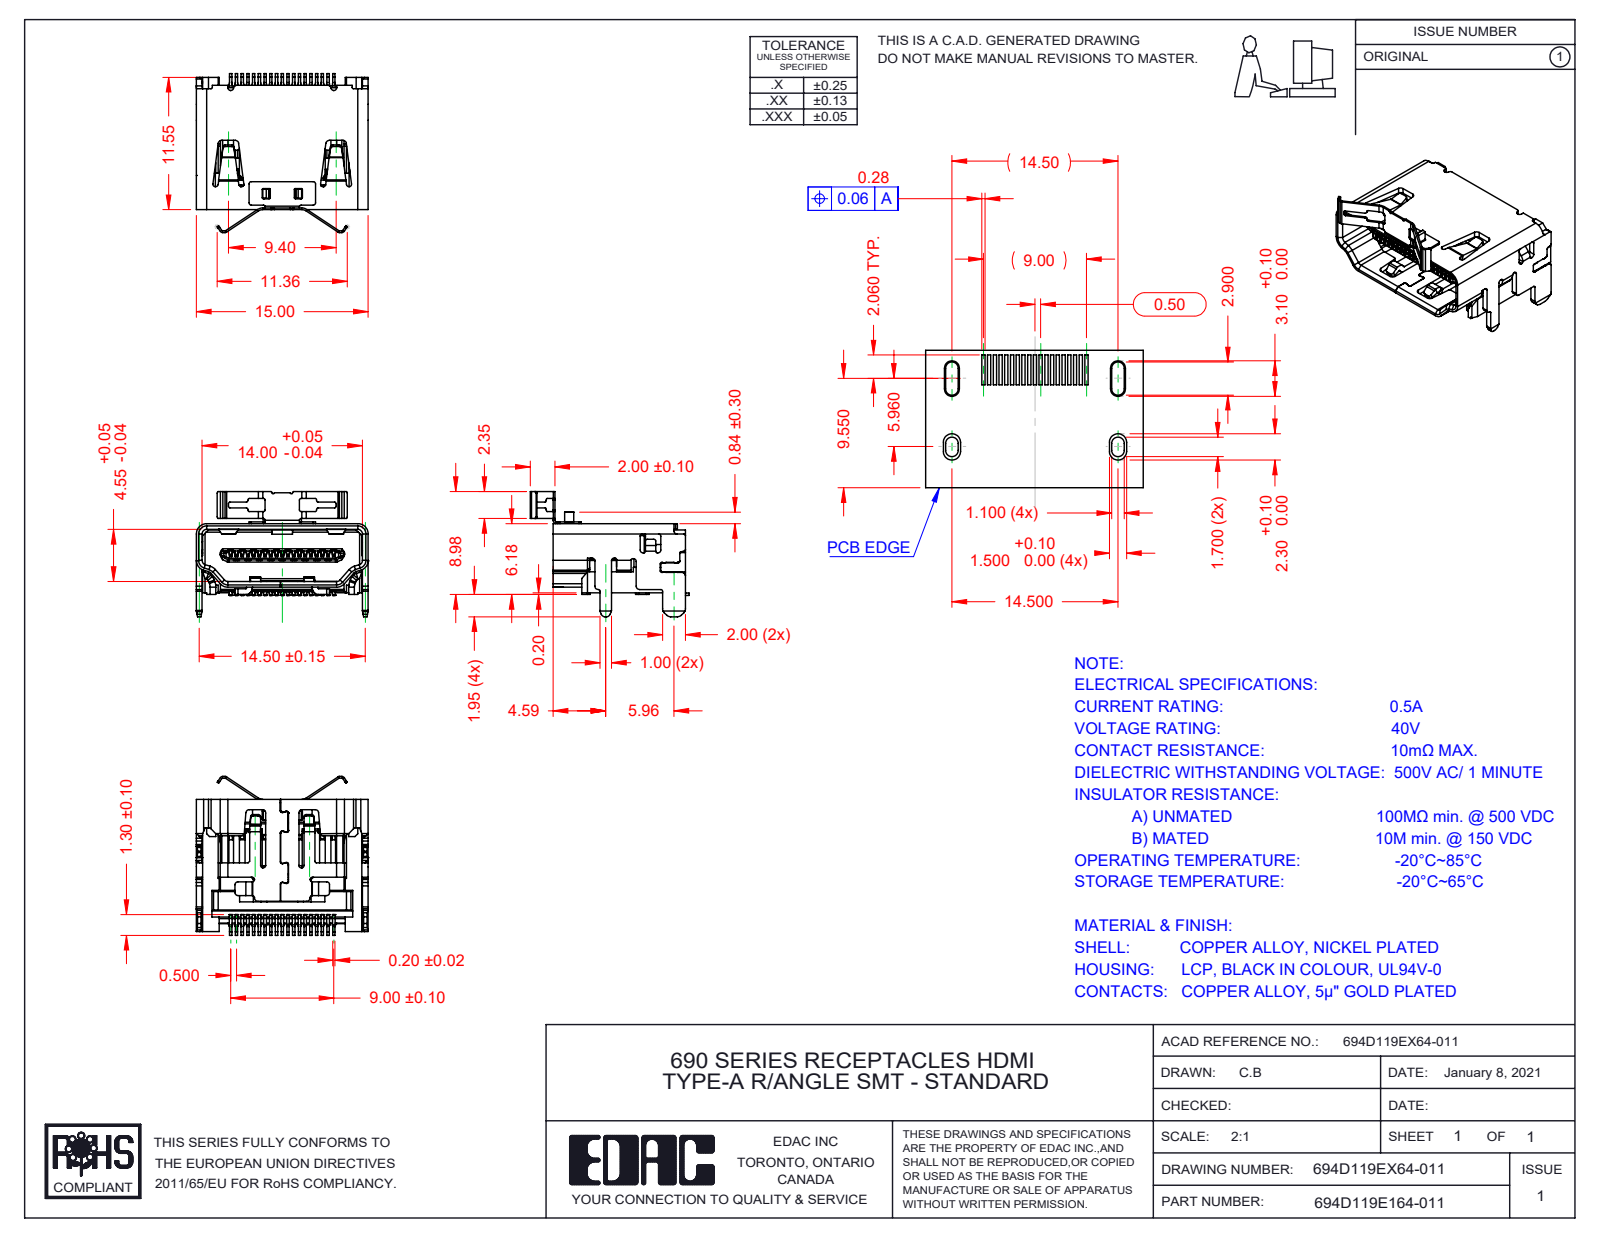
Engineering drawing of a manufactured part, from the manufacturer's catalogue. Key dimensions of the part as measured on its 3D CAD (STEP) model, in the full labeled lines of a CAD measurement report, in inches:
Part name (STEP PRODUCT): Shell 694D119EX64-011; Contacts 694D119EX64-011; Insulator 694D119EX64-011; EMI 694D119EX64-011 (+1 more)
STEP written by: SolidWorks 2020 (AUTOMOTIVE_DESIGN)
Units: inches
Bodies: 22 solids, 3527 faces (2264 planar, 1188 cylindrical, 75 other)
Overall size (bounding box): 0.591 × 0.546 × 0.43
Volume: 0.028 in³ · Surface area: 2.953 in²
Partial cylindrical surfaces — rounded edges, fillets, slot ends (radius × count): R0.008 ×120, R0.006 ×111, R0.004 ×66, R0.005 ×30, R0.012 ×23, R0.01 ×22, R0.004 ×20, R0.009 ×10
Main face-to-face distances: 0.02, 0.1, 0.028, 0.022, 0.019, 0.08, 0.571, 0.072, 0.014, 0.199
